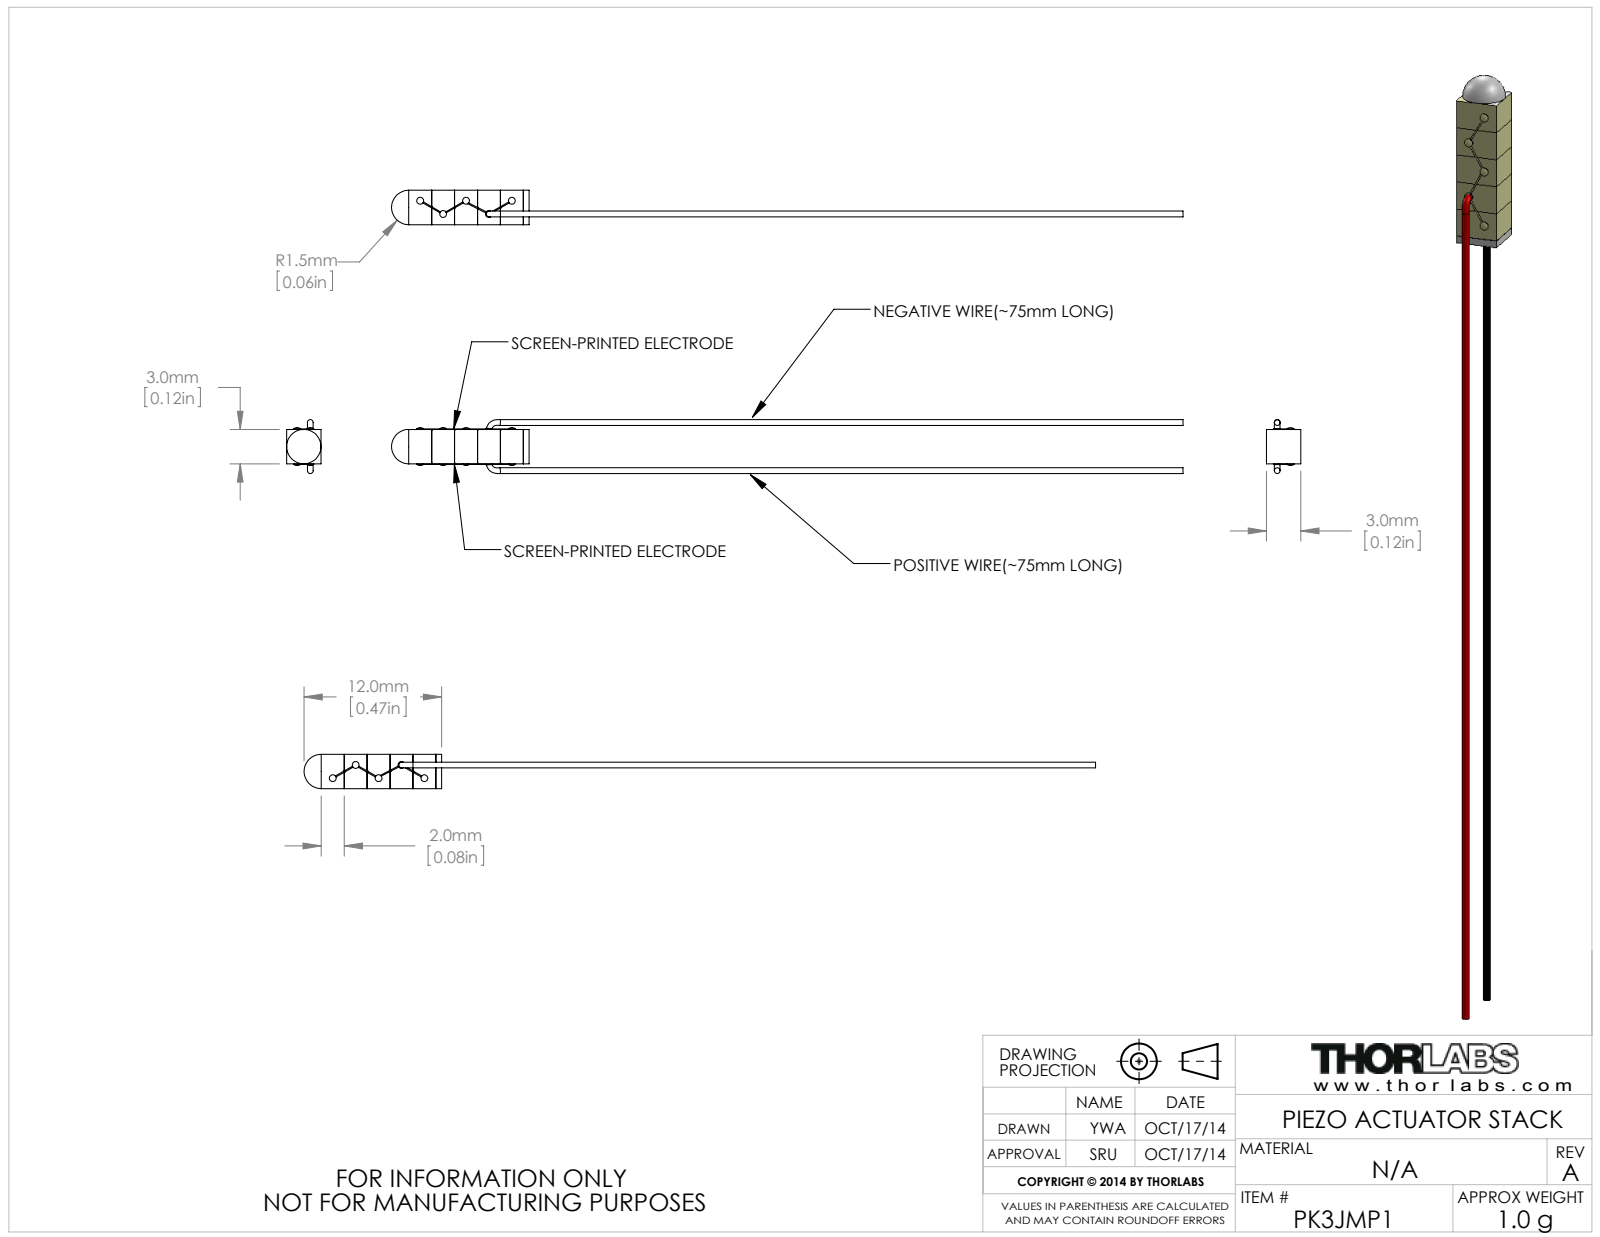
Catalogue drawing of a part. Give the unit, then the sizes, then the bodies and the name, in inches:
Units: inches
Overall size (bounding box): 2.72 × 0.186 × 0.118
Round bosses / shafts (diameter × count): ⌀0.024 ×5
Main face-to-face distances: 0.079, 0.118, 0.157, 0.236, 0.315, 0.02, 0.099, 0.178, 0.256, 0.335
Volume: 0.008 in³ · Surface area: 0.674 in²
Bodies: 2 solids, 123 faces (47 planar, 46 cylindrical, 30 other)
Part name (STEP PRODUCT): PK3JMP1
STEP written by: SolidWorks 2012 (AUTOMOTIVE_DESIGN)
